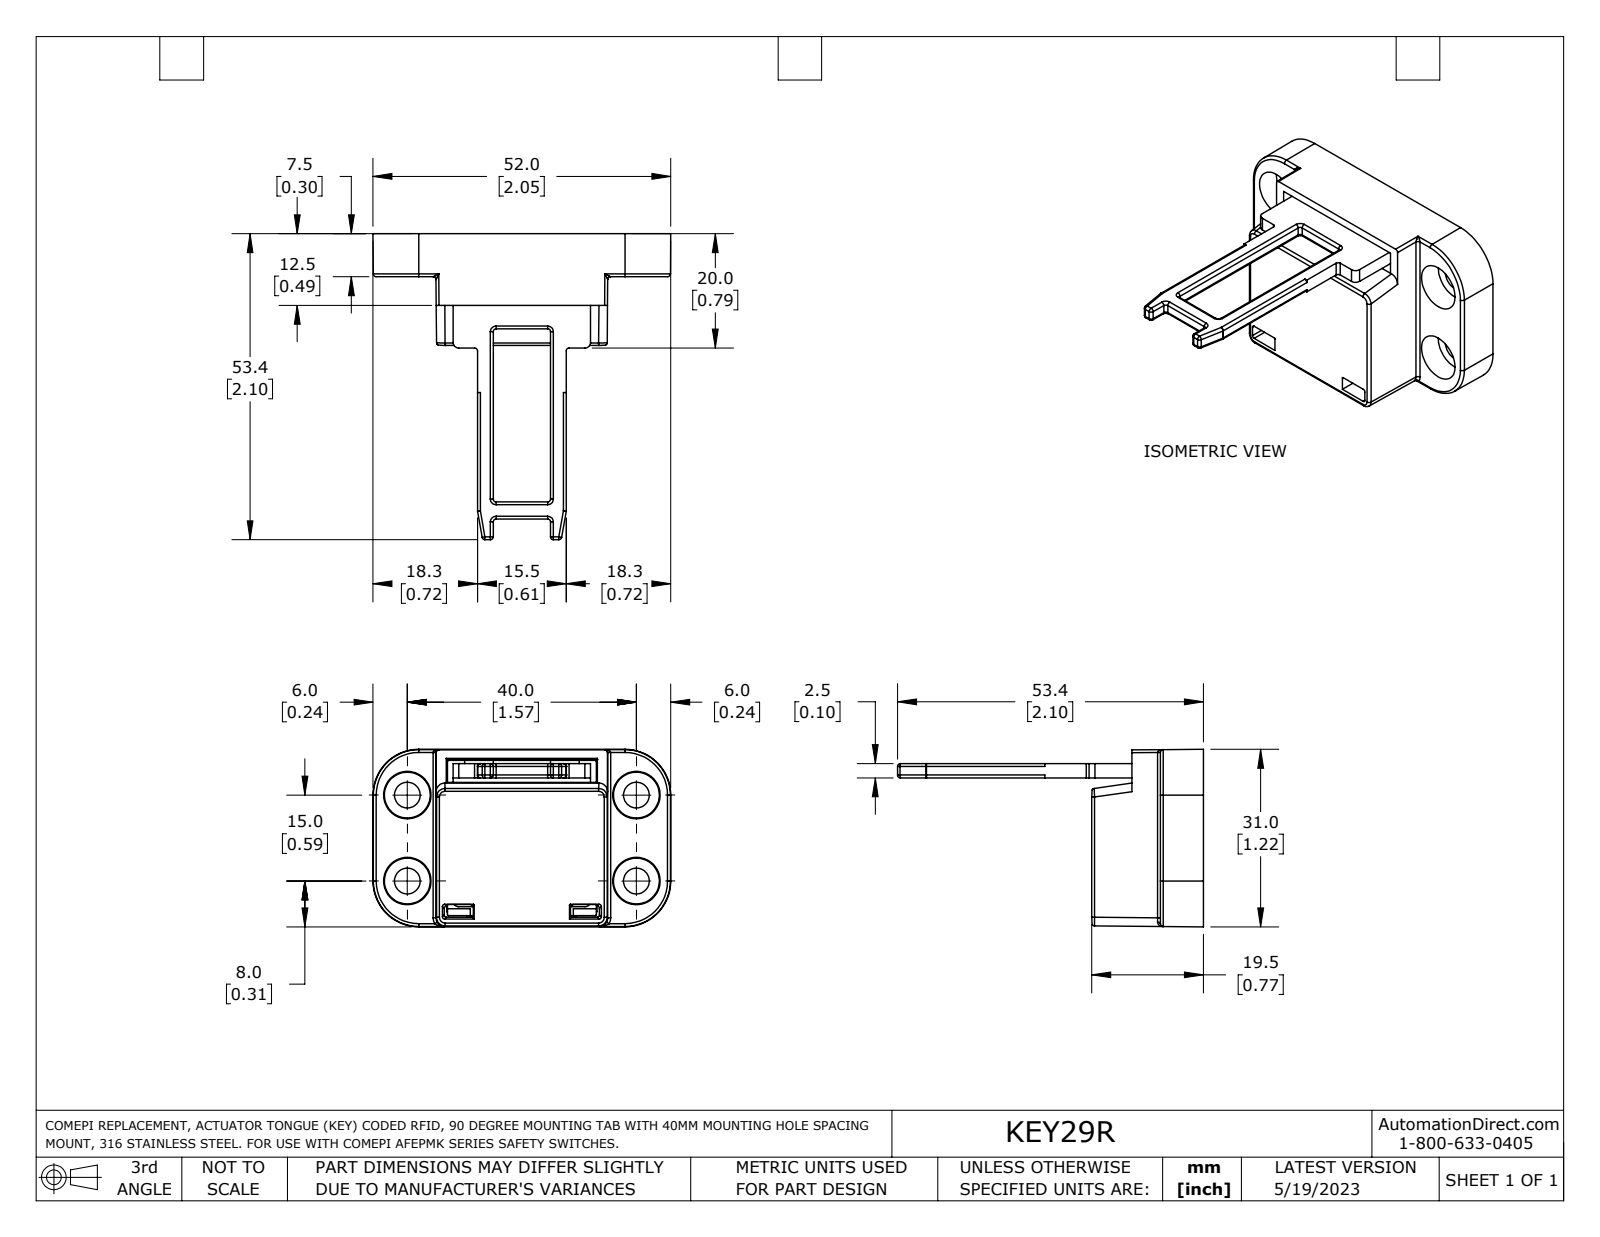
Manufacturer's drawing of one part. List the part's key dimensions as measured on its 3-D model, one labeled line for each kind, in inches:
Part name (STEP PRODUCT): KEY29R
STEP written by: SolidWorks 2021 (AUTOMOTIVE_DESIGN)
Units: inches
Bodies: 1 solid, 343 faces (171 planar, 76 cylindrical, 96 other)
Overall size (bounding box): 2.103 × 2.047 × 1.22
Volume: 0.762 in³ · Surface area: 20.46 in²
Round holes (diameter × count): ⌀0.197 ×1
Round bosses / shafts (diameter × count): ⌀0.346 ×1
Partial cylindrical surfaces — rounded edges, fillets, slot ends (radius × count): R0.02 ×46, R0.008 ×4, R0.016 ×4, R0.039 ×4, R0.059 ×4, R0.006 ×2, R0.031 ×1, R0.13 ×1
Main face-to-face distances: 0.079, 0.689, 0.098, 0.276, 0.02, 0.768, 0.315, 0.217, 0.453, 0.236
